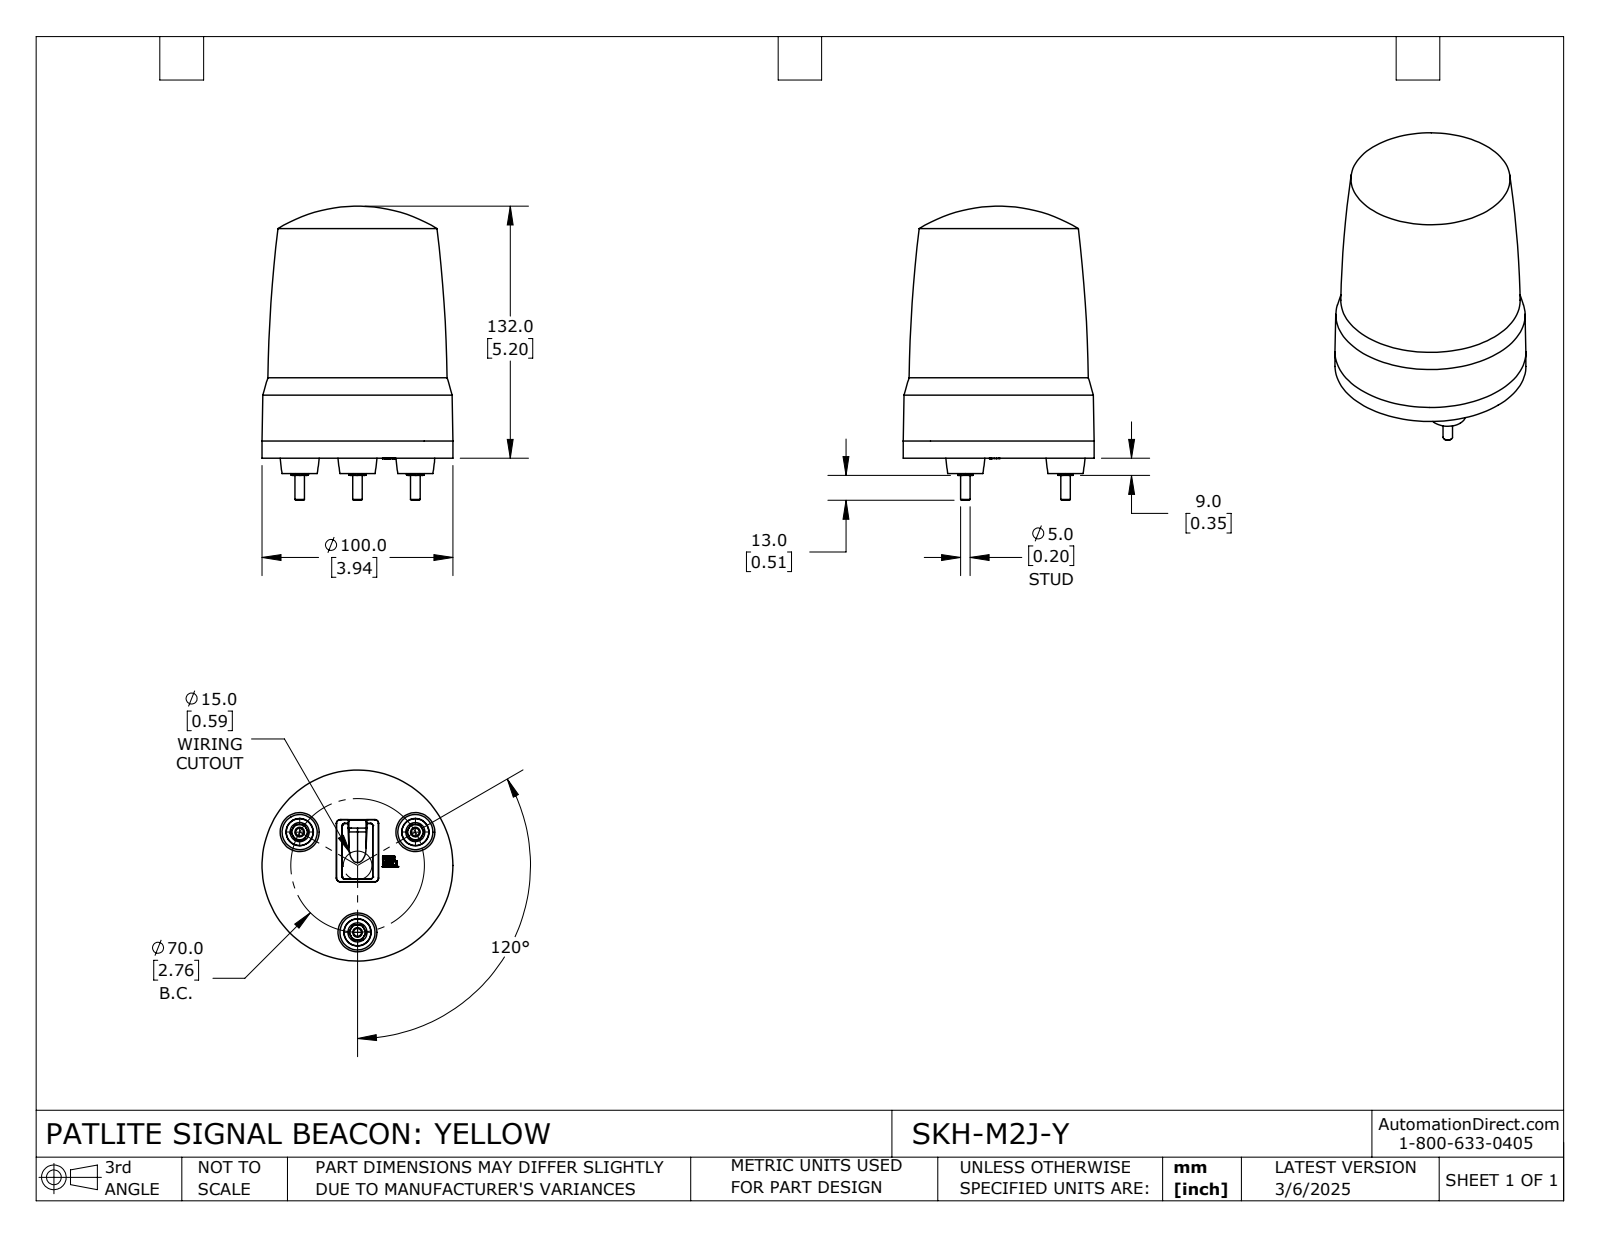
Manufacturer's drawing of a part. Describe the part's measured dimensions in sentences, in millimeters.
The part is named "SKH-M2J-Y". Its 3-D file was written by "SolidWorks 2024 (CONFIG_CONTROL_DESIGN)". It is 1 solid with 327 faces: 159 planar, 14 cylindrical and 154 other. Overall it measures 154 by 100 by 100 millimeters. Its volume is 859 960 cubic millimeters and its surface area 52 586 square millimeters. Round bosses or shafts: 3 of diameter 10, 3 of diameter 5, 1 of diameter 100. The main face-to-face distances are 8, 0.85, 8.85, 1.6, 10.45, 2.45, 3.8, 4.2, 5.05, 6.65.
